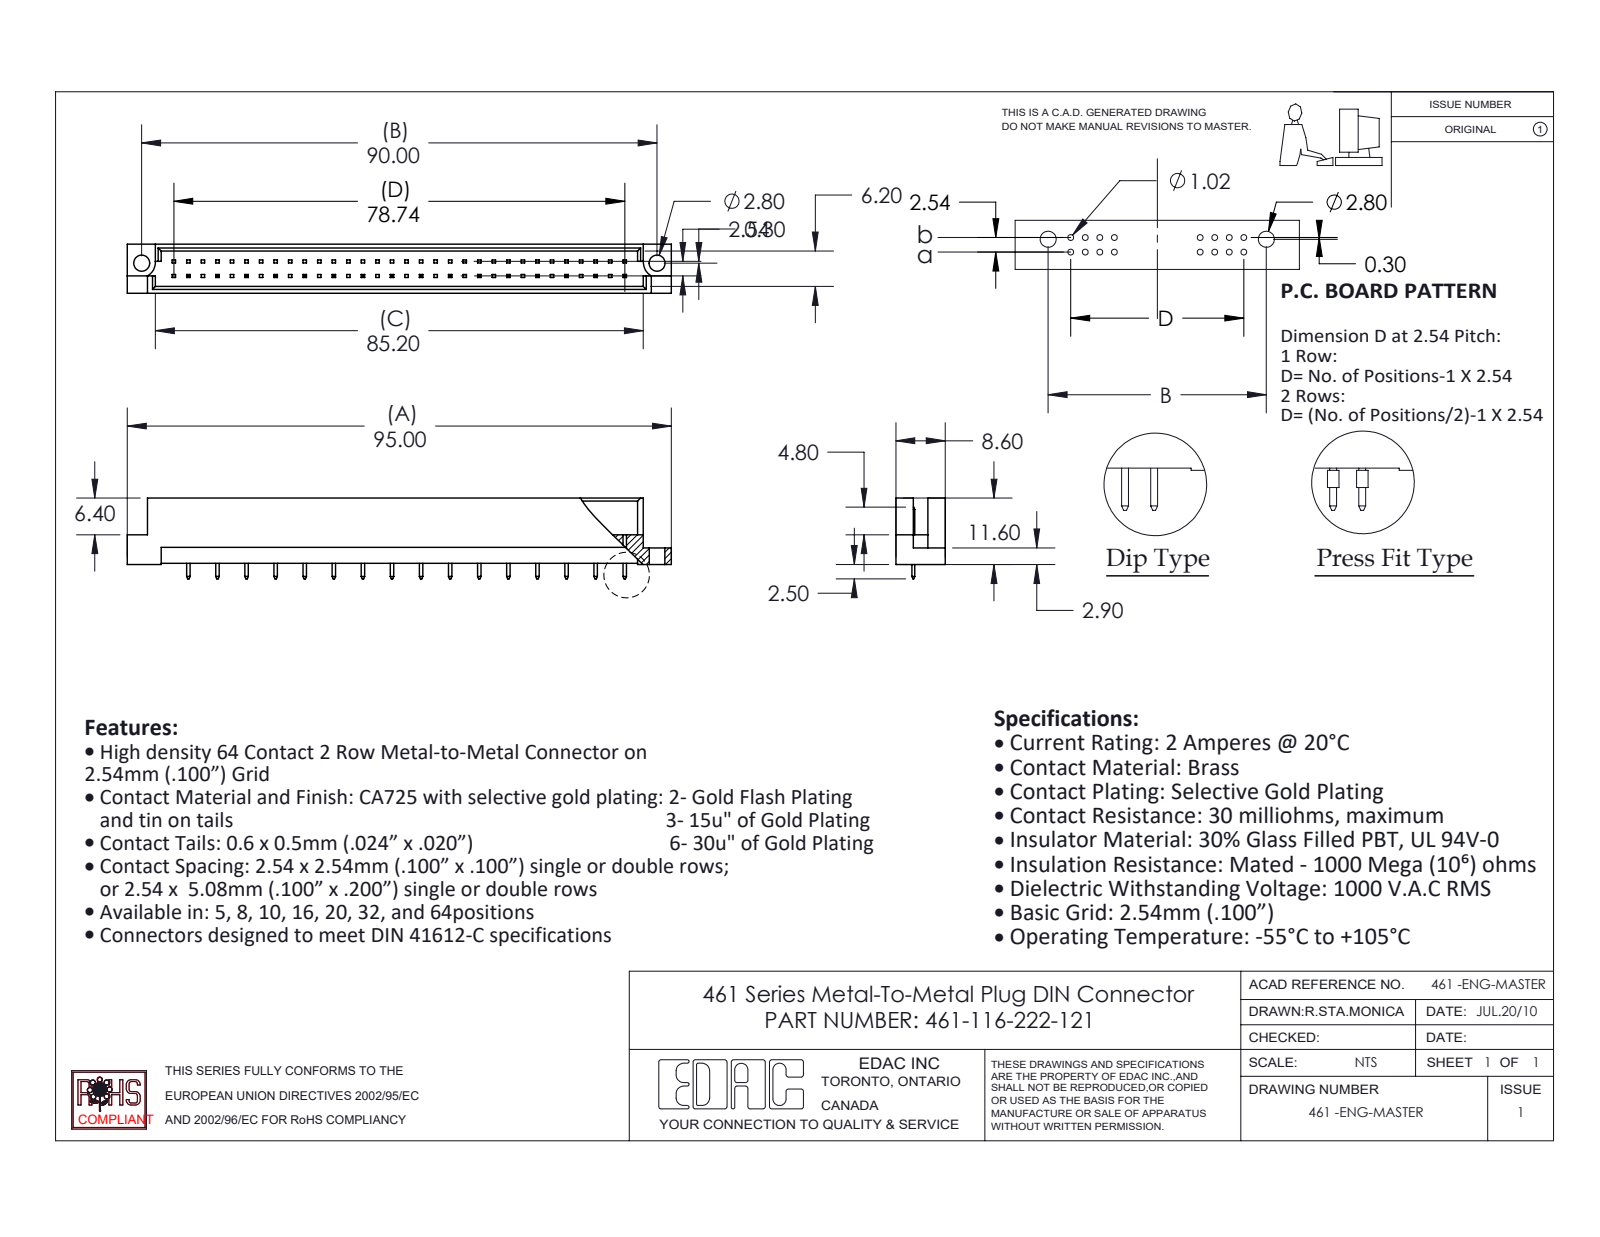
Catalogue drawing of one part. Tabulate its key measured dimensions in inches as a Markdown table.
| quantity | value |
| --- | --- |
| part name | 461-116-222-221; 461 Part_64; 461-290_22 |
| STEP written by | SolidWorks 2020 (CONFIG_CONTROL_DESIGN) |
| units | inches |
| bodies | 17 solids, 529 faces (522 planar, 7 cylindrical, 0 other) |
| overall size | 3.74 × 0.555 × 0.339 |
| volume | 0.288 in³ |
| surface area | 9.464 in² |
| round holes (diameter × count) | 0.11 × 2 |
| partial cylindrical surfaces (radius × count) | 0.11 × 2 |
| main face-to-face distances | 0.047, 0.291, 0.339, 0.244, 0.197, 0.129, 0.209, 0.082, 0.162, 0.109 |
| hole center spacings | 3.543 |
